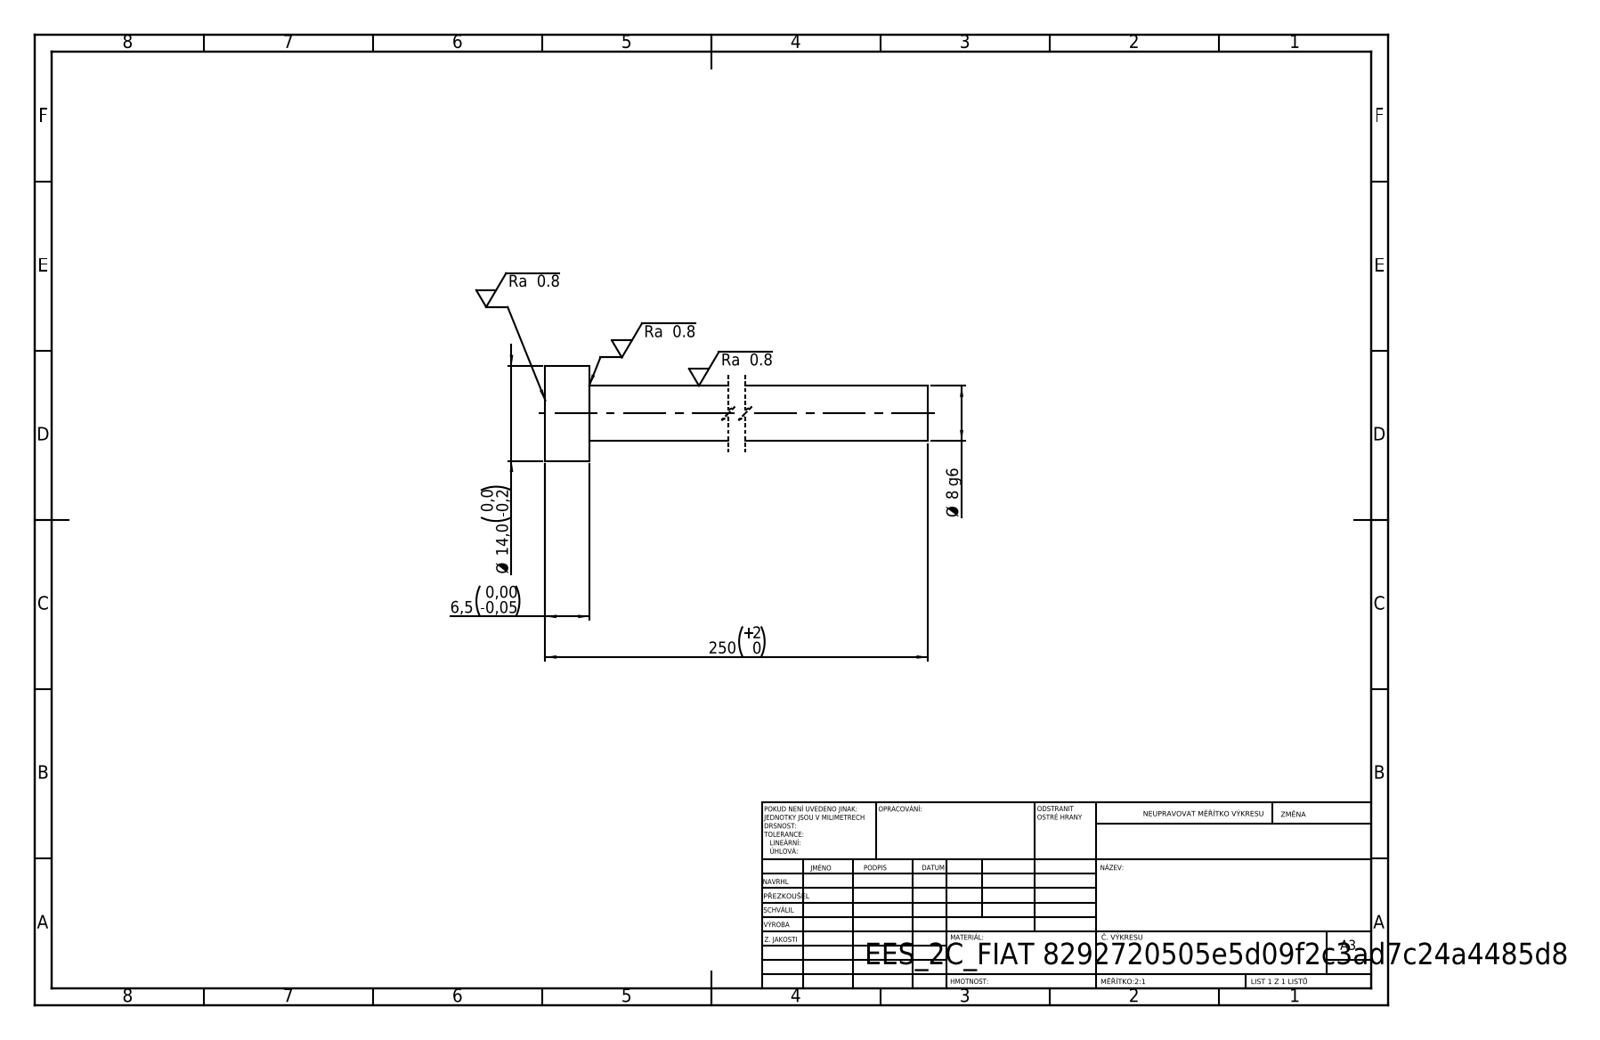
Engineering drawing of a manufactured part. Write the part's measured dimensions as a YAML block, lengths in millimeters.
step_written_by: "SolidWorks 2019 (CONFIG_CONTROL_DESIGN)"
units: millimeters
bodies: {solids: 1, faces: 7, planar: 3, cylindrical: 4, other: 0}
overall_size: [250, 14, 14]
volume: 13860
surface_area: 6867
round_bosses_or_shafts:
  - {diameter: 14, count: 1}
  - {diameter: 8.2, count: 1}
face_to_face_distances: [6.5, 250, 243.5]
